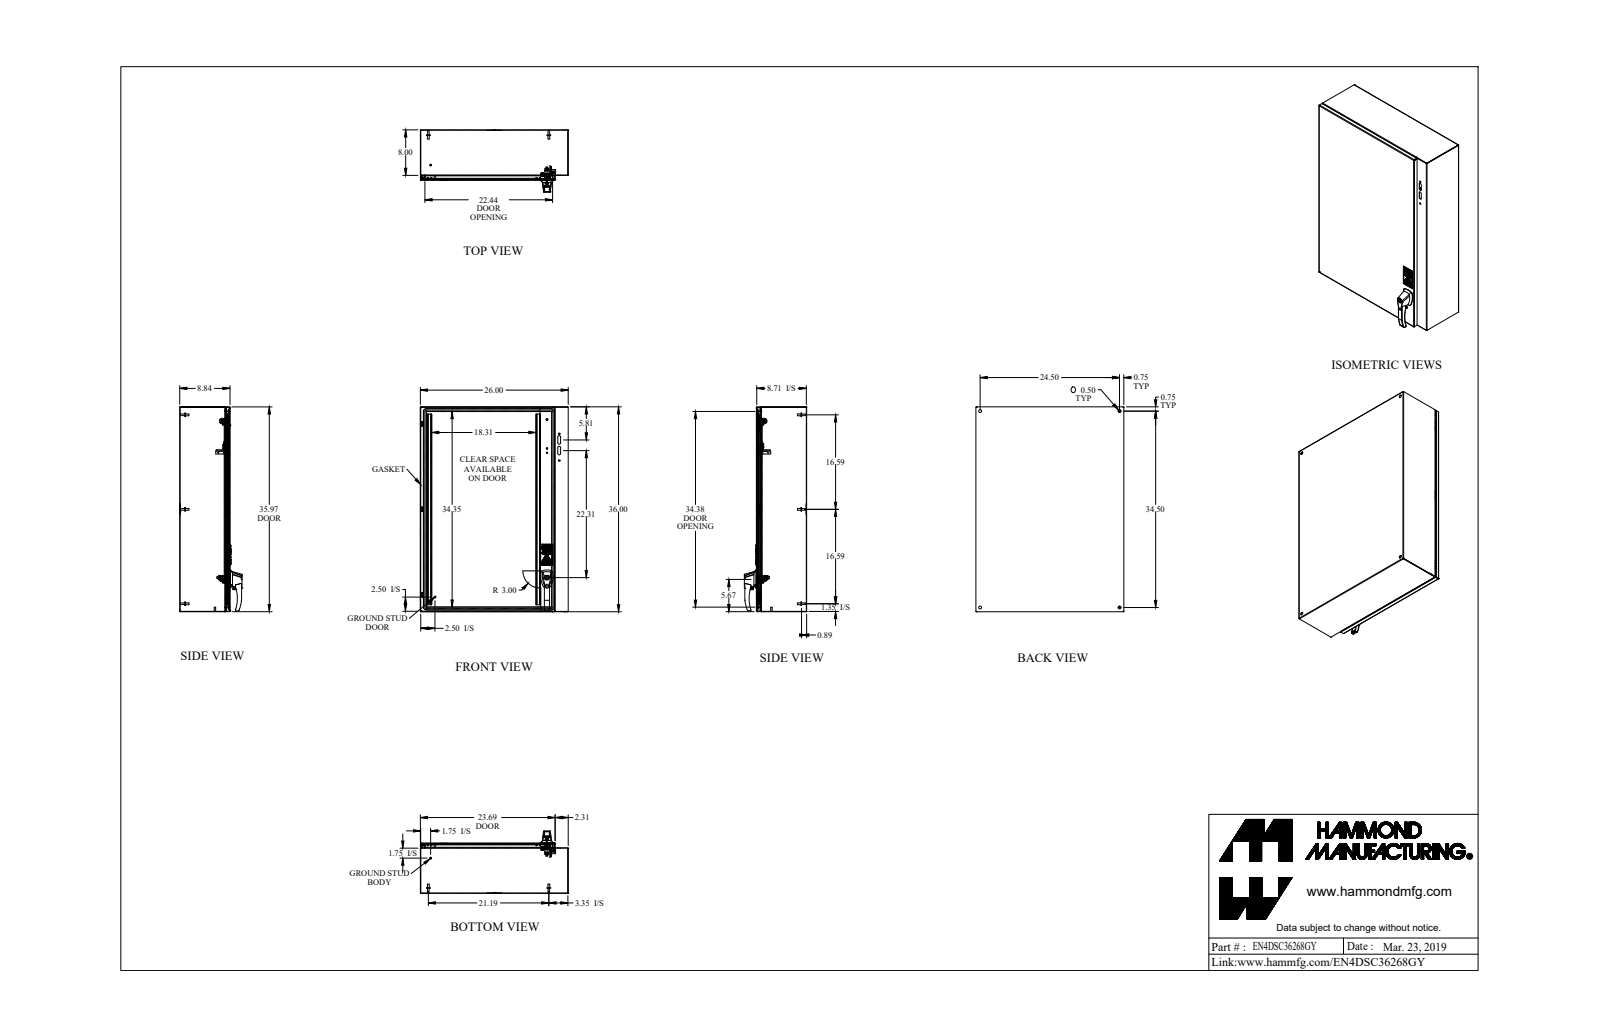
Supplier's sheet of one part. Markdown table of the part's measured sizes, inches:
| quantity | value |
| --- | --- |
| part name | EN4DSC36268GY |
| STEP written by | SolidWorks 2019 (AUTOMOTIVE_DESIGN) |
| units | inches |
| bodies | 53 solids, 1085 faces (581 planar, 341 cylindrical, 163 other) |
| overall size | 36 × 26 × 10.952 |
| volume | 224.1 in³ |
| surface area | 6 882 in² |
| round holes (diameter × count) | 0.176 × 4, 0.156 × 2, 0.173 × 2, 0.215 × 2, 0.25 × 2, 0.265 × 2, 0.281 × 2, 0.413 × 2, 0.172 × 1, 0.196 × 1, 0.233 × 1, 0.24 × 1 |
| round bosses / shafts (diameter × count) | 0.25 × 7, 0.313 × 6, 0.27 × 6, 0.375 × 4, 0.156 × 4, 0.625 × 3, 0.625 × 3, 1 × 2 |
| partial cylindrical surfaces (radius × count) | 0.079 × 28, 0.022 × 16, 0.25 × 14, 0.043 × 12, 0.081 × 12, 0.125 × 11, 0.136 × 8, 0.006 × 6 |
| main face-to-face distances | 0.057, 8.708, 8.765, 0.072, 8.78, 8.837, 25.943, 35.943, 26, 25.886 |
| hole center spacings | 27.75, 1.11, 0.52, 0.75, 0.817, 0.992, 1.004, 1.139 |
